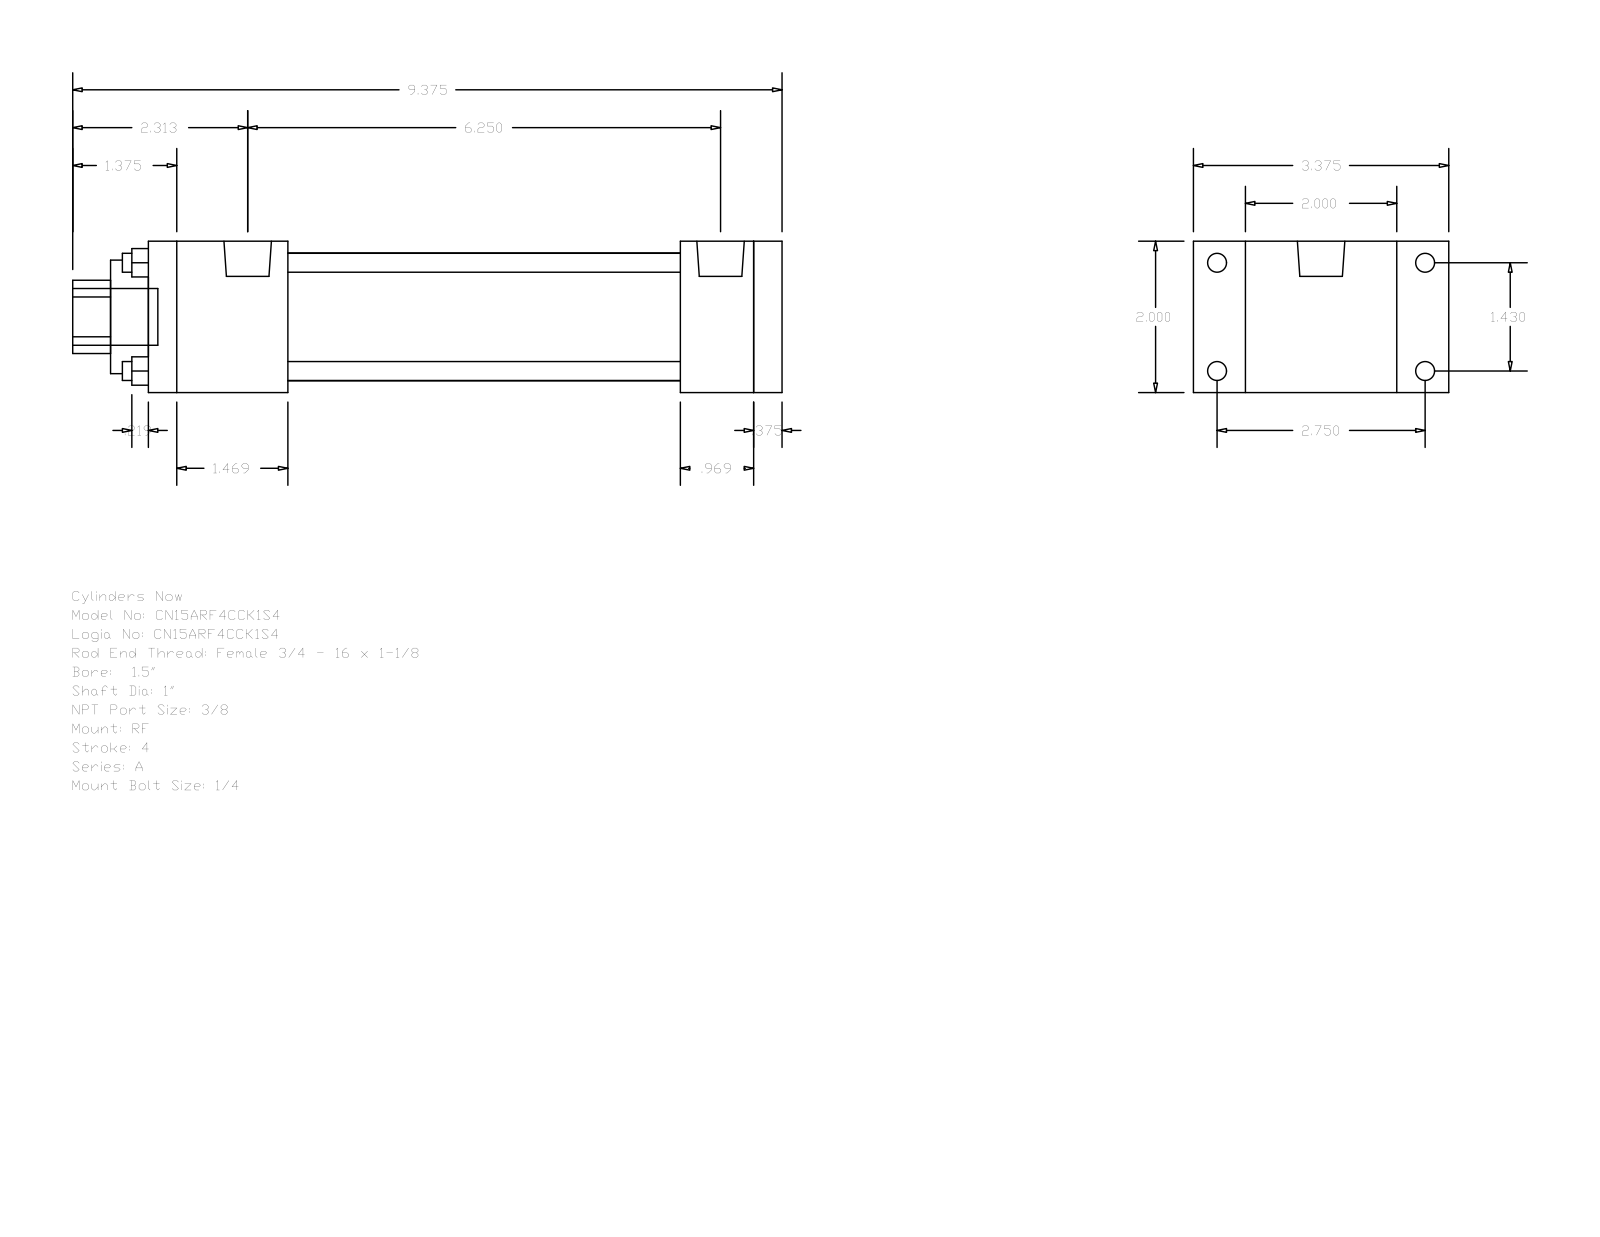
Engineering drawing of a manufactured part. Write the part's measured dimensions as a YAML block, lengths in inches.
part_name: "A_RF__0150_1"
step_written_by: "GSSL Pune (CONFIG_CONTROL_DESIGN)"
units: inches
bodies: {solids: 0, faces: 92, planar: 64, cylindrical: 28, other: 0}
overall_size: [9.375, 3.375, 2]
round_holes:
  - {diameter: 0.25, count: 4}
  - {diameter: 1, count: 1}
  - {diameter: 1.5, count: 1}
  - {diameter: 1.69, count: 1}
round_bosses_or_shafts:
  - {diameter: 0.25, count: 4}
  - {diameter: 0.219, count: 4}
  - {diameter: 0.627, count: 2}
  - {diameter: 0.75, count: 1}
partial_cylinders:
  - {radius: 0.484, count: 1}
face_to_face_distances: [2, 0.375, 8, 8.375, 7.031, 0.969, 1.344, 1.844, 5.187, 6.156]
hole_center_spacings: [1.011, 1.43, 2.022]
